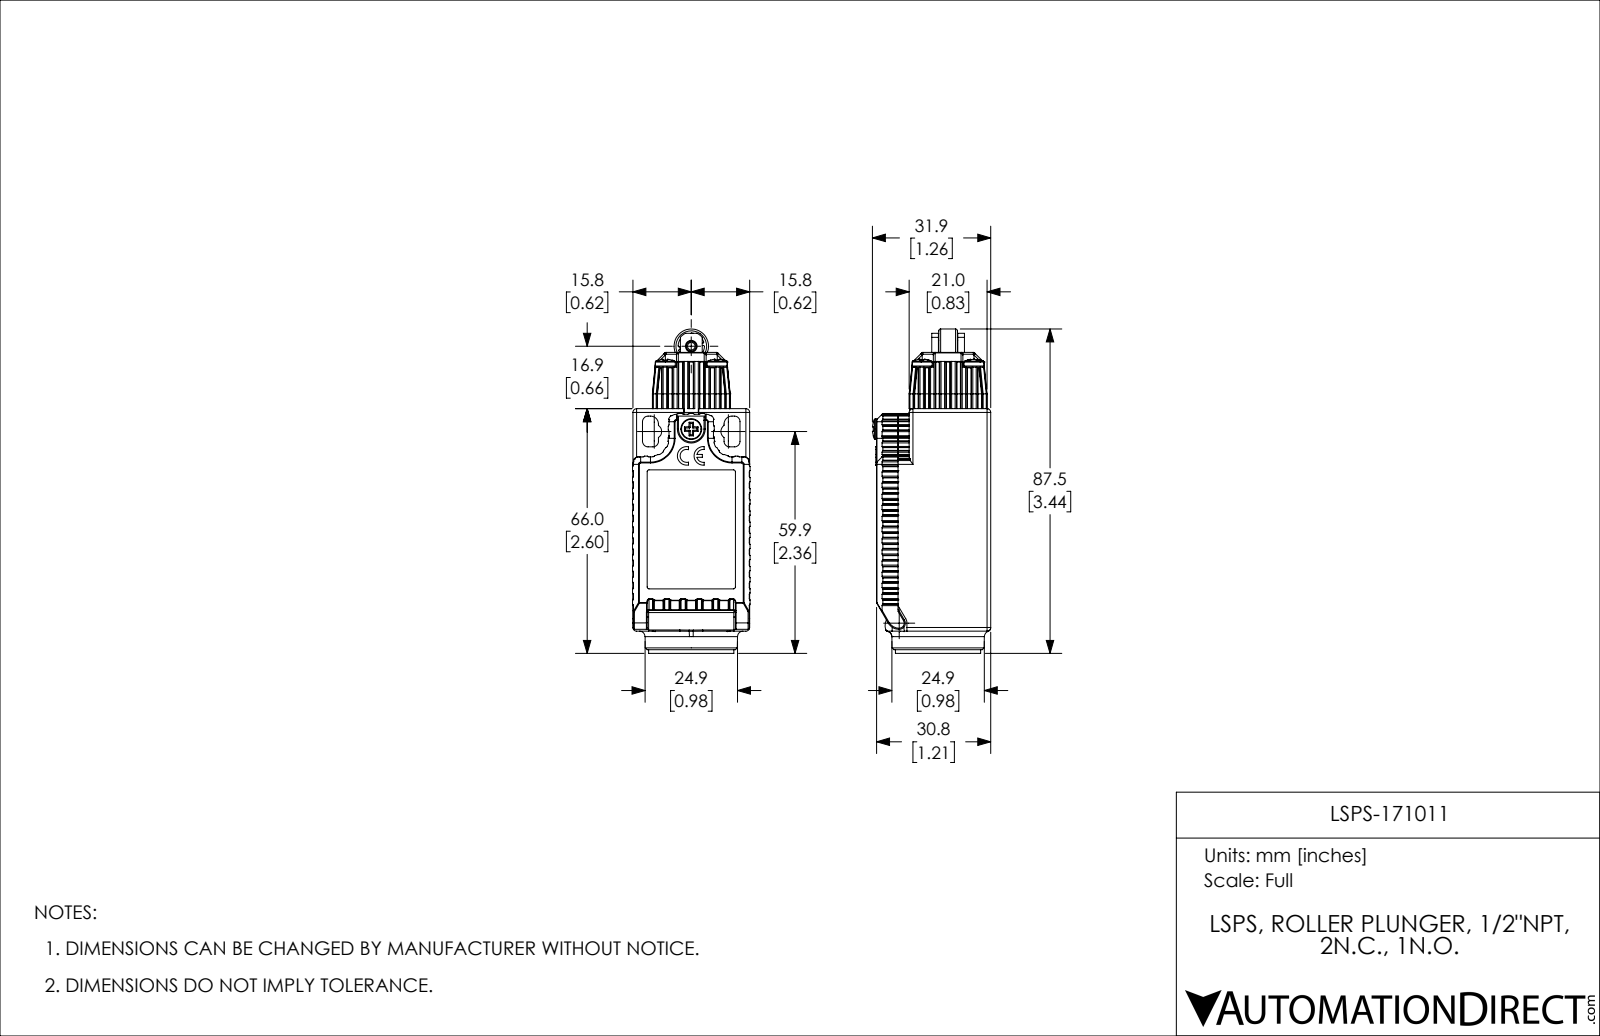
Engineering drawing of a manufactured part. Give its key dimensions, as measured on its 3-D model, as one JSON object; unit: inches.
{"part_name": "LSPS-171011", "step_written_by": "SolidWorks 2017 (AUTOMOTIVE_DESIGN)", "units": "inches", "bodies": {"solids": 15, "faces": 2867, "planar": 1314, "cylindrical": 1176, "other": 377}, "overall_size": [3.445, 1.257, 1.248], "volume_in3": 1.761, "surface_area_in2": 45.94, "round_holes": [[0.091, 5], [0.102, 4], [0.126, 4], [0.217, 4], [0.157, 2], [0.081, 1], [0.098, 1], [0.124, 1], [0.134, 1], [0.146, 1], [0.197, 1], [0.244, 1]], "round_bosses_or_shafts": [[0.067, 5], [0.213, 4], [0.098, 4], [0.906, 1], [0.717, 1], [0.618, 1], [0.61, 1], [0.441, 1]], "partial_cylinders_radius": [[0.02, 253], [0.008, 132], [0.004, 92], [0.012, 61], [0.013, 32], [0.039, 23], [0.079, 14], [0.024, 9]], "face_to_face_distances": [0.089, 1.152, 1.24, 0.063, 1.102, 0.039, 0.102, 1.063, 0.22, 1.165], "hole_center_spacings": [0.39, 0.551, 0.306, 0.324, 0.471, 0.646, 0.78, 0.787]}
